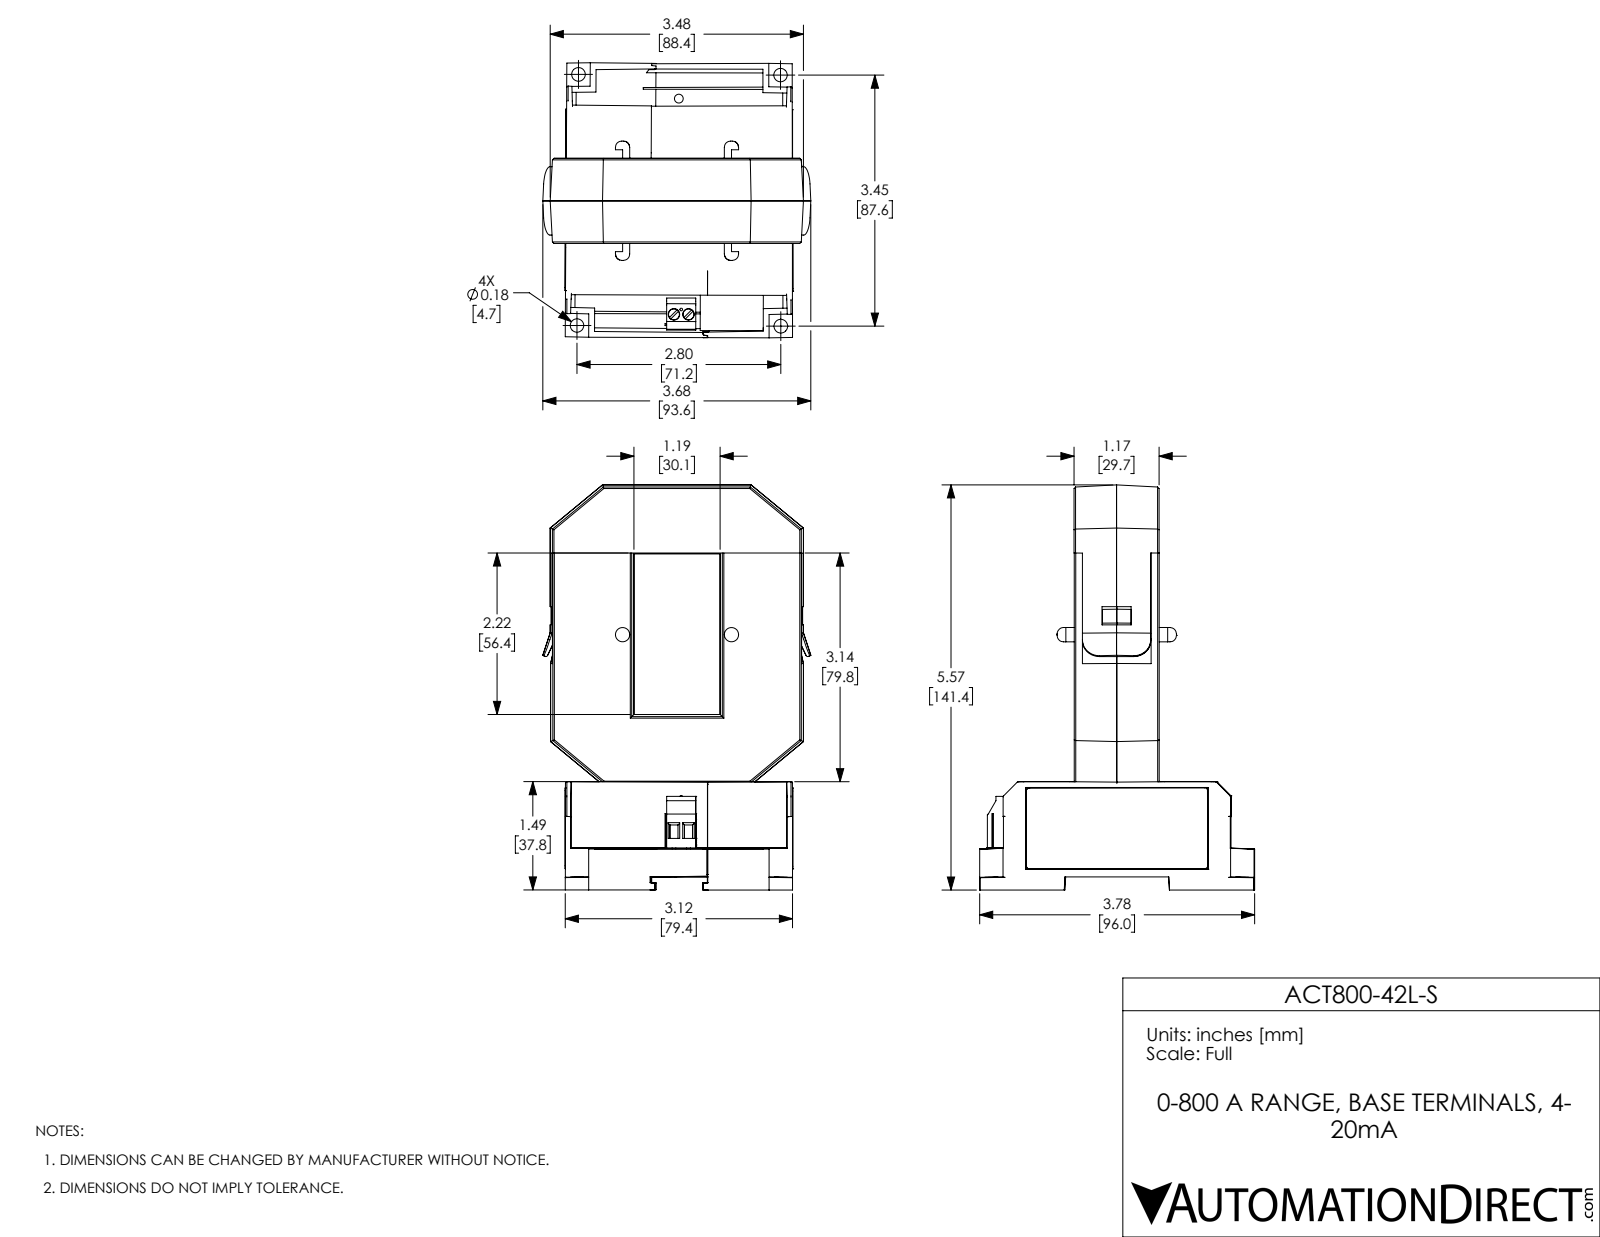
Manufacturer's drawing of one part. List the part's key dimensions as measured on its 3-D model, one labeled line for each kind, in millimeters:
Part name (STEP PRODUCT): ACT800-42L-S
STEP written by: SolidWorks 2017 (AUTOMOTIVE_DESIGN)
Units: millimetres
Bodies: 15 solids, 1439 faces (1182 planar, 144 cylindrical, 113 other)
Overall size (bounding box): 141.5 × 96 × 93.6
Volume: 131 000 mm³ · Surface area: 143 600 mm²
Round holes (diameter × count): ⌀4 ×2, ⌀6.5 ×2
Round bosses / shafts (diameter × count): ⌀5 ×2, ⌀3.8 ×2, ⌀1.3 ×2, ⌀0.5 ×1
Partial cylindrical surfaces — rounded edges, fillets, slot ends (radius × count): R0.5 ×30, R1 ×12, R0.2 ×10, R1.3 ×8, R0.6 ×6, R0.2 ×4, R0.3 ×4, R0.5 ×4
Main face-to-face distances: 1.8, 27.9, 29.7, 26.1, 2.1, 14.9, 1.9, 2, 59.1, 27.8
Hole centre spacings: 5.1, 10.7, 39.7, 39.9, 40.2, 40.7
